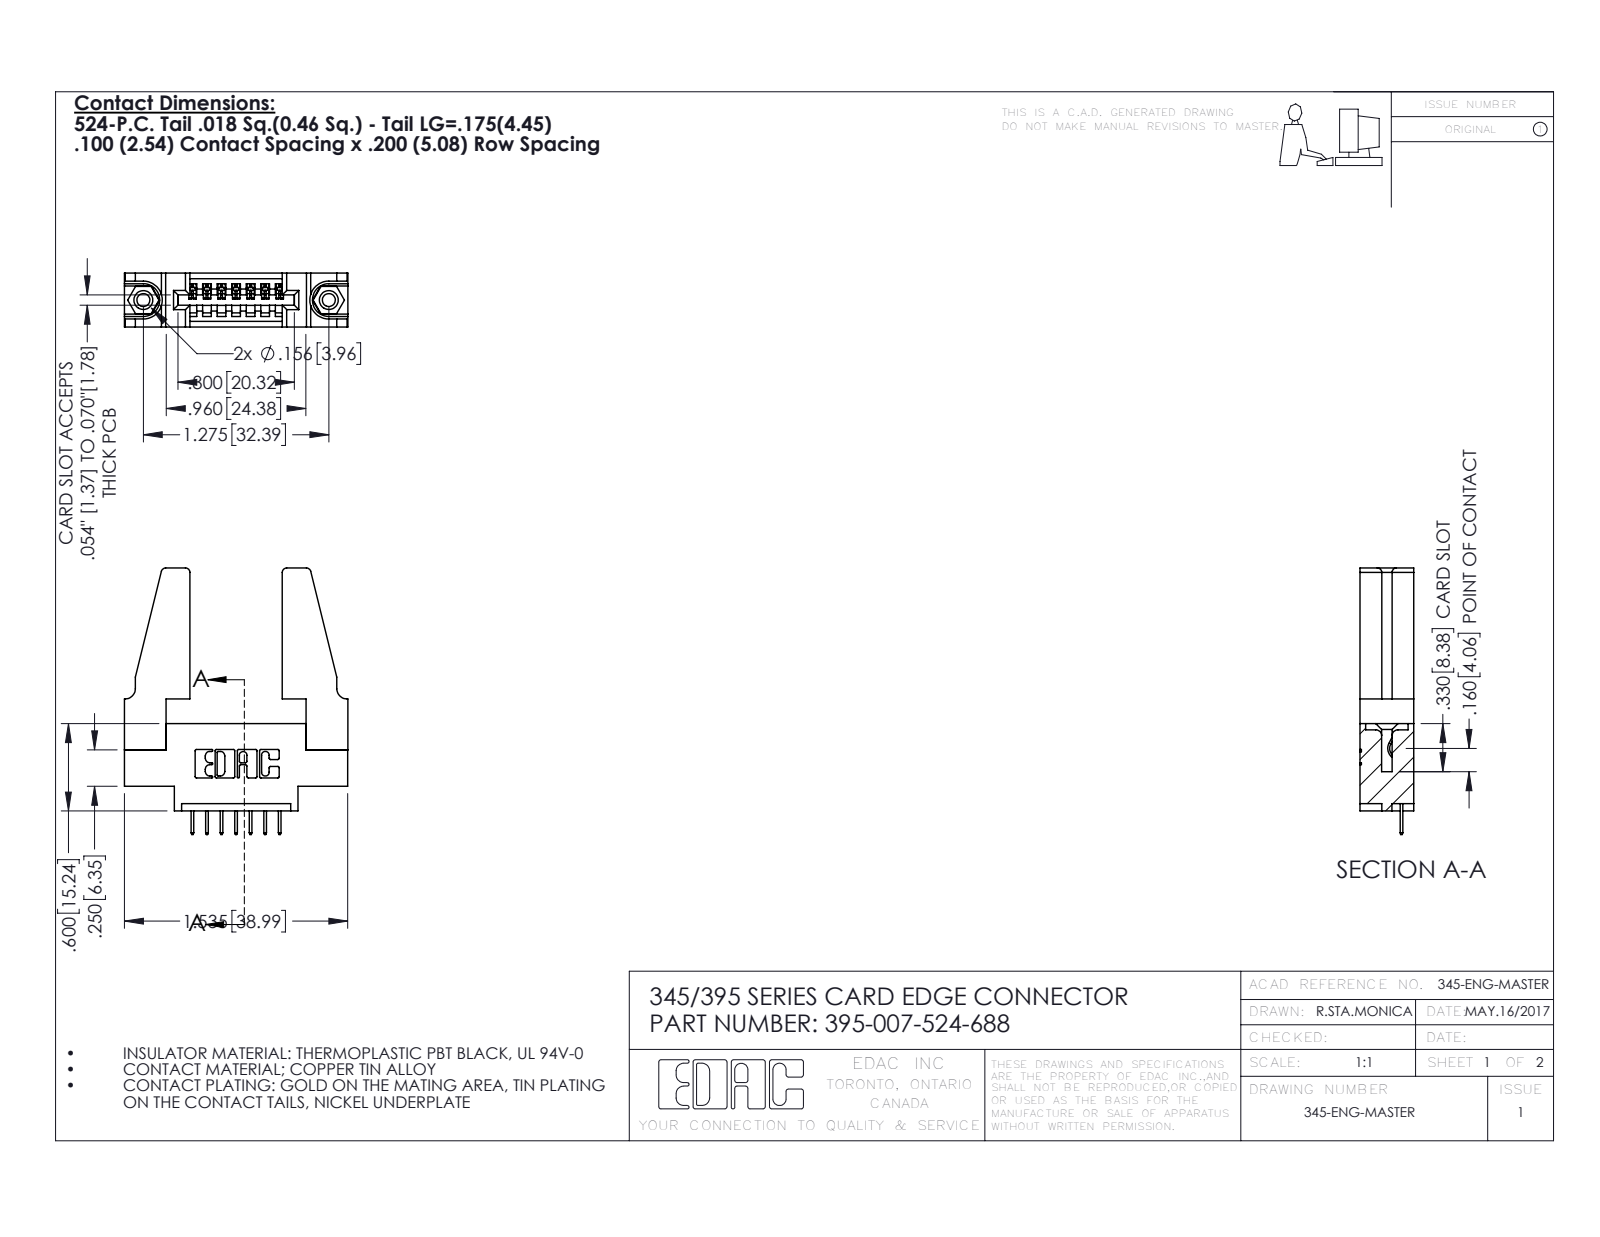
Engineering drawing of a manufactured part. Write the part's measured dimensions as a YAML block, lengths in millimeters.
part_name: "345 Part_0.170 Offset - 0.156 Dia-TH; 345-220-078_345-220-088; 345-250-001_345-250-001-102; 345-292-001_345-293-124 (+1 more)"
step_written_by: "SolidWorks 2016 (CONFIG_CONTROL_DESIGN)"
units: millimeters
bodies: {solids: 12, faces: 688, planar: 478, cylindrical: 194, other: 16}
overall_size: [46.5, 39, 9.4]
volume: 6540
surface_area: 7045
round_holes:
  - {diameter: 2.3, count: 2}
  - {diameter: 3.2, count: 2}
  - {diameter: 4, count: 2}
  - {diameter: 1.6, count: 1}
round_bosses_or_shafts:
  - {diameter: 3.9, count: 2}
partial_cylinders:
  - {radius: 0.3, count: 22}
  - {radius: 0.2, count: 14}
  - {radius: 0.8, count: 8}
  - {radius: 0.2, count: 6}
  - {radius: 0.8, count: 6}
  - {radius: 0.7, count: 3}
  - {radius: 0.8, count: 2}
  - {radius: 1, count: 2}
face_to_face_distances: [9.4, 1.8, 7.6, 3.8, 3.8, 5.1, 2.5, 6.9, 0.6, 5.6]
hole_center_spacings: [6.9, 26.5, 32.4]
